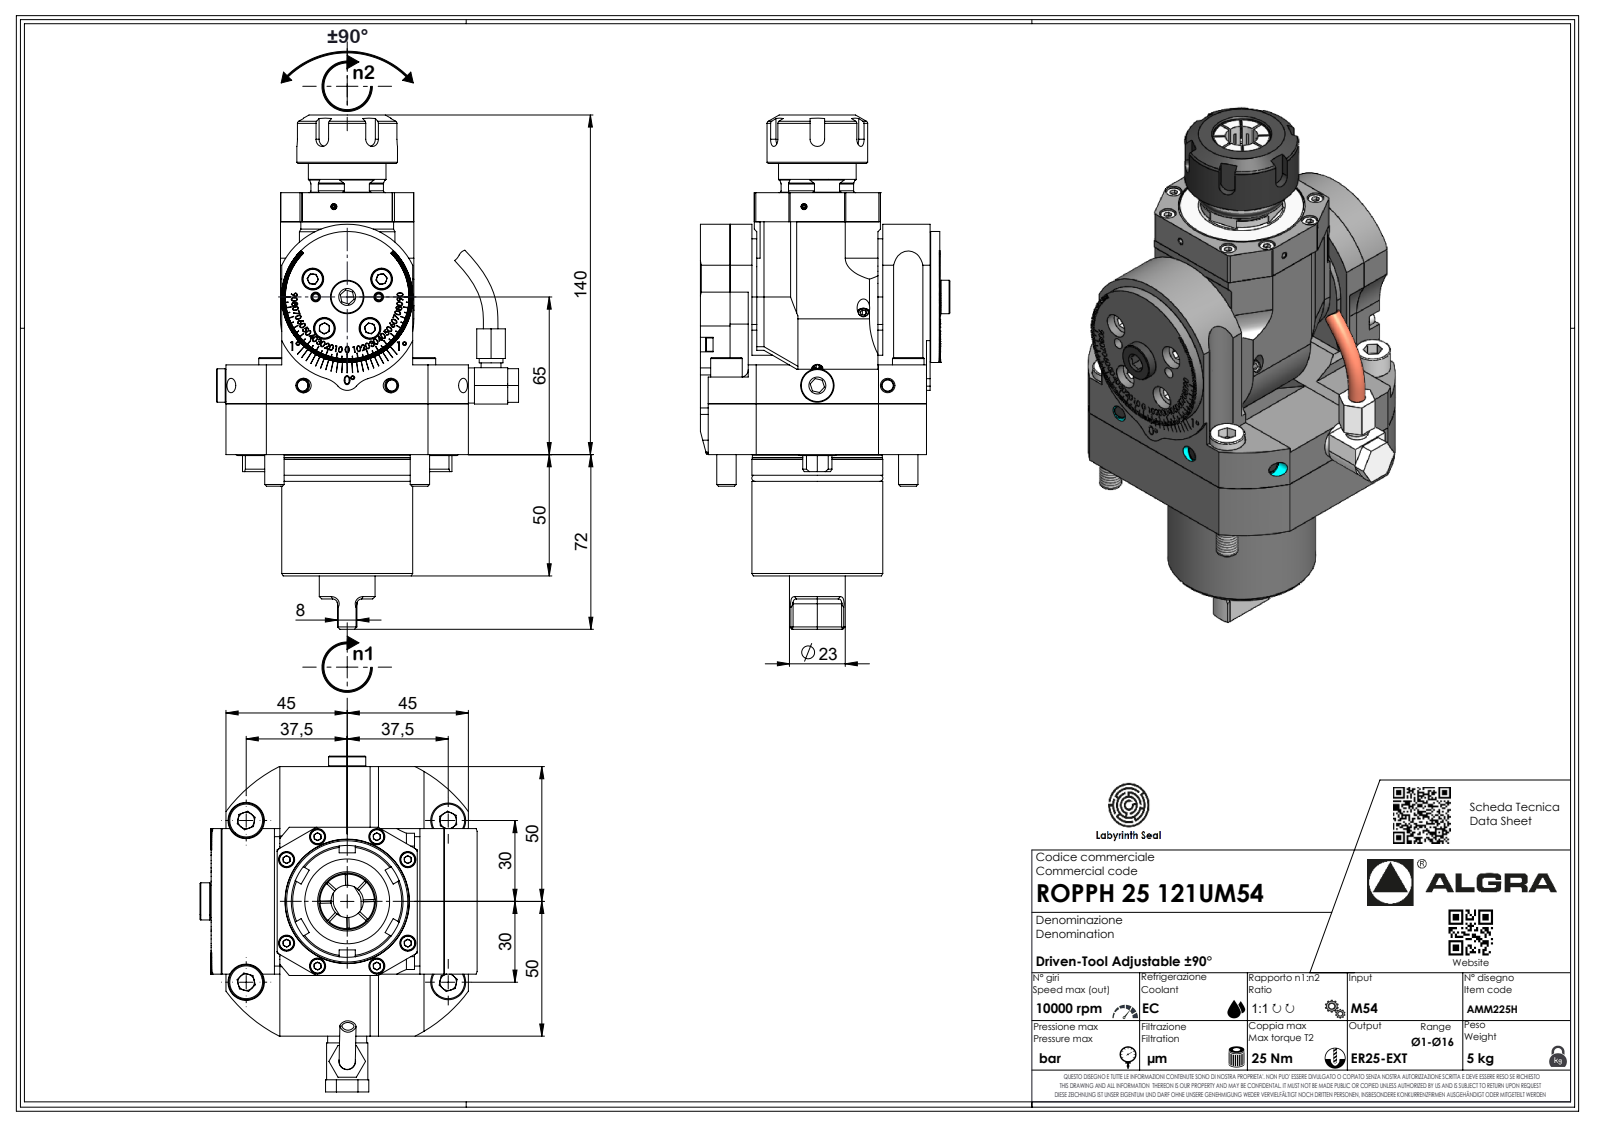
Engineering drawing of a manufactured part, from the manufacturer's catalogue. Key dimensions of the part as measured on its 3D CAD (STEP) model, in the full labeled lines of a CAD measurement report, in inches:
Part name (STEP PRODUCT): ROPPH25121UM54
STEP written by: SolidWorks 2023 (AUTOMOTIVE_DESIGN)
Units: inches
Bodies: 1 solid, 621 faces (407 planar, 118 cylindrical, 96 other)
Overall size (bounding box): 8.348 × 4.752 × 3.888
Volume: 47.12 in³ · Surface area: 118.3 in²
Round holes (diameter × count): ⌀0.083 ×1
Round bosses / shafts (diameter × count): ⌀2.126 ×2, ⌀2.11 ×1, ⌀1.965 ×1, ⌀1.634 ×1, ⌀1.26 ×1, ⌀0.906 ×1, ⌀0.571 ×1, ⌀0.386 ×1
Partial cylindrical surfaces — rounded edges, fillets, slot ends (radius × count): R0.039 ×8, R0.394 ×8, R0.013 ×7, R0.02 ×7, R0.146 ×7, R0.079 ×6, R0.118 ×6, R0.197 ×5
Main face-to-face distances: 0.02, 3.051, 2.146, 3.031, 0.906, 1.969, 2.795, 0.886, 3.888, 0.217
